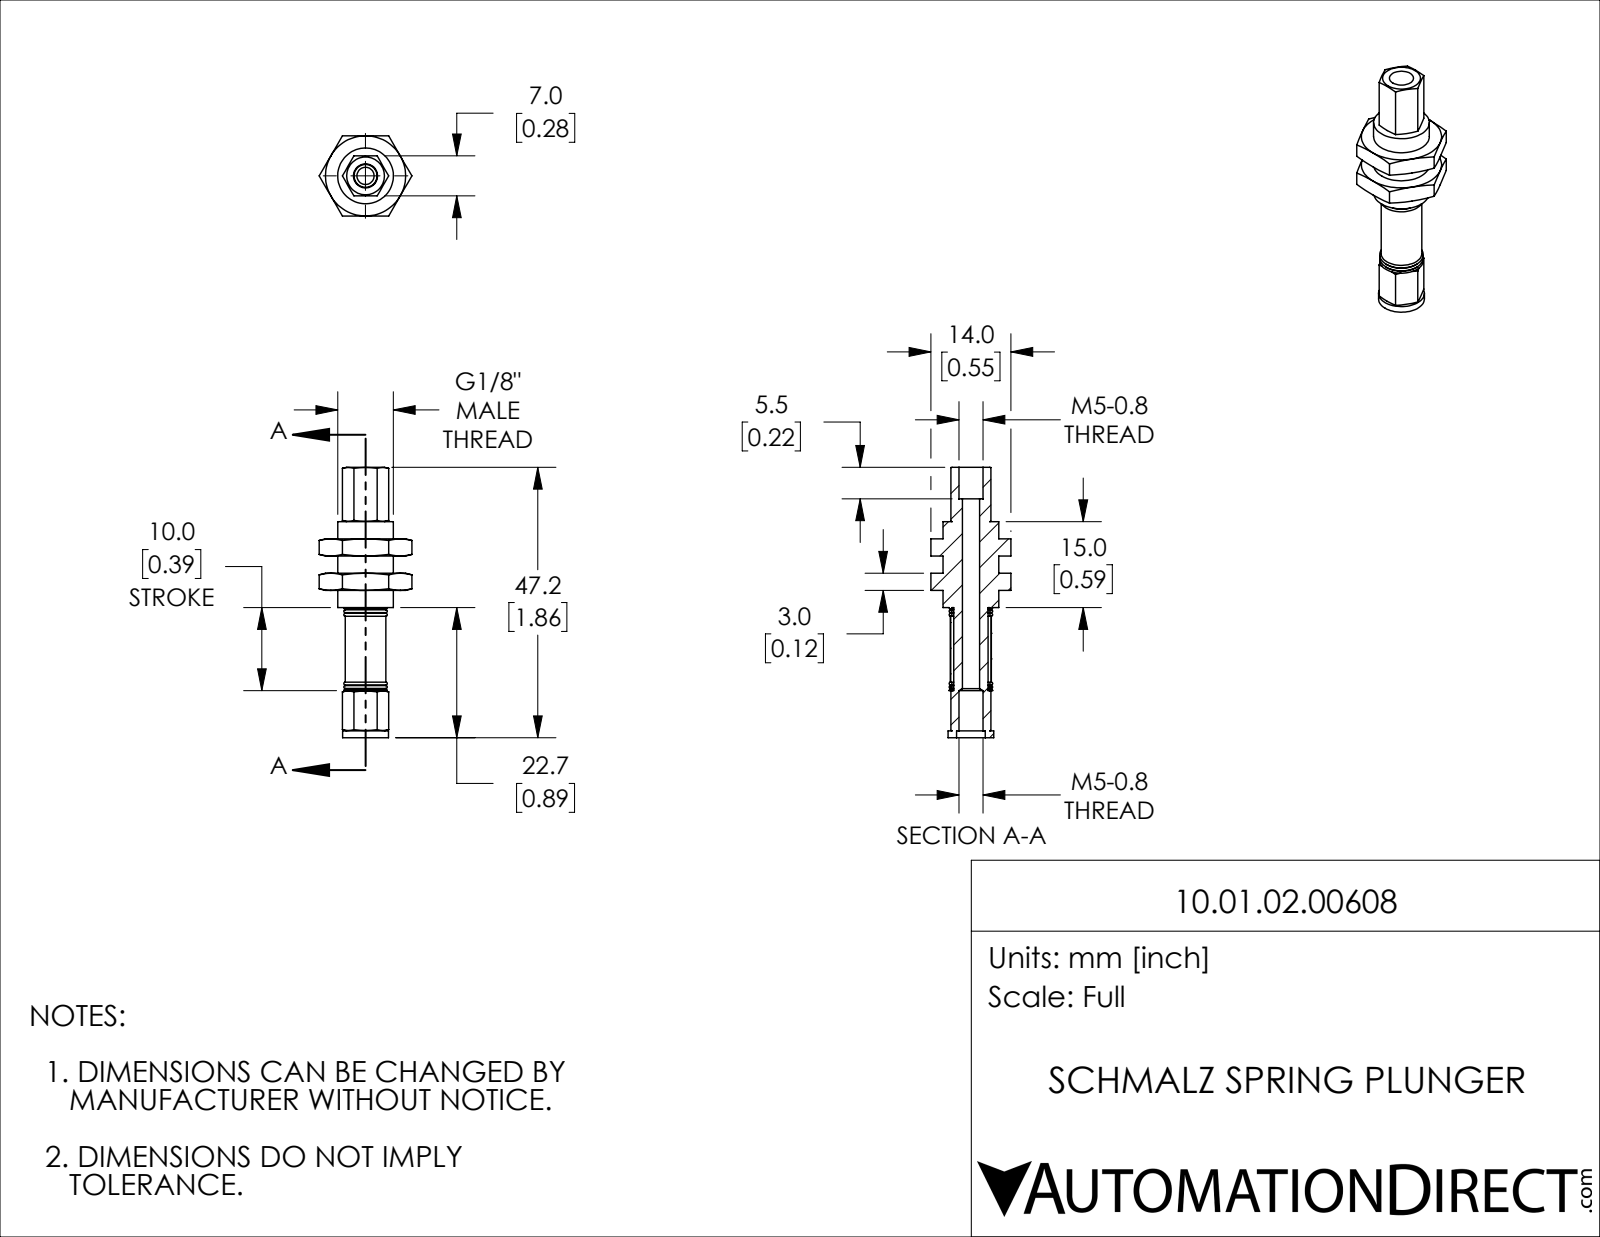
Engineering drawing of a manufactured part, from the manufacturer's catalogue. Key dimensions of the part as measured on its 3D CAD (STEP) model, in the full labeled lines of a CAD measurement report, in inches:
Part name (STEP PRODUCT): 10.01.02.00608
STEP written by: SolidWorks 2021 (CONFIG_CONTROL_DESIGN)
Units: inches
Bodies: 1 solid, 148 faces (38 planar, 38 cylindrical, 72 other)
Overall size (bounding box): 1.858 × 0.637 × 0.551
Volume: 0.149 in³ · Surface area: 4.721 in²
Round holes (diameter × count): ⌀0.118 ×1, ⌀0.165 ×1, ⌀0.197 ×1, ⌀0.28 ×1
Round bosses / shafts (diameter × count): ⌀0.383 ×1, ⌀0.315 ×1, ⌀0.28 ×1, ⌀0.236 ×1
Main face-to-face distances: 0.118, 0.138, 0.413, 0.236, 0.276, 0.354, 0.551, 0.472, 0.846, 0.965
